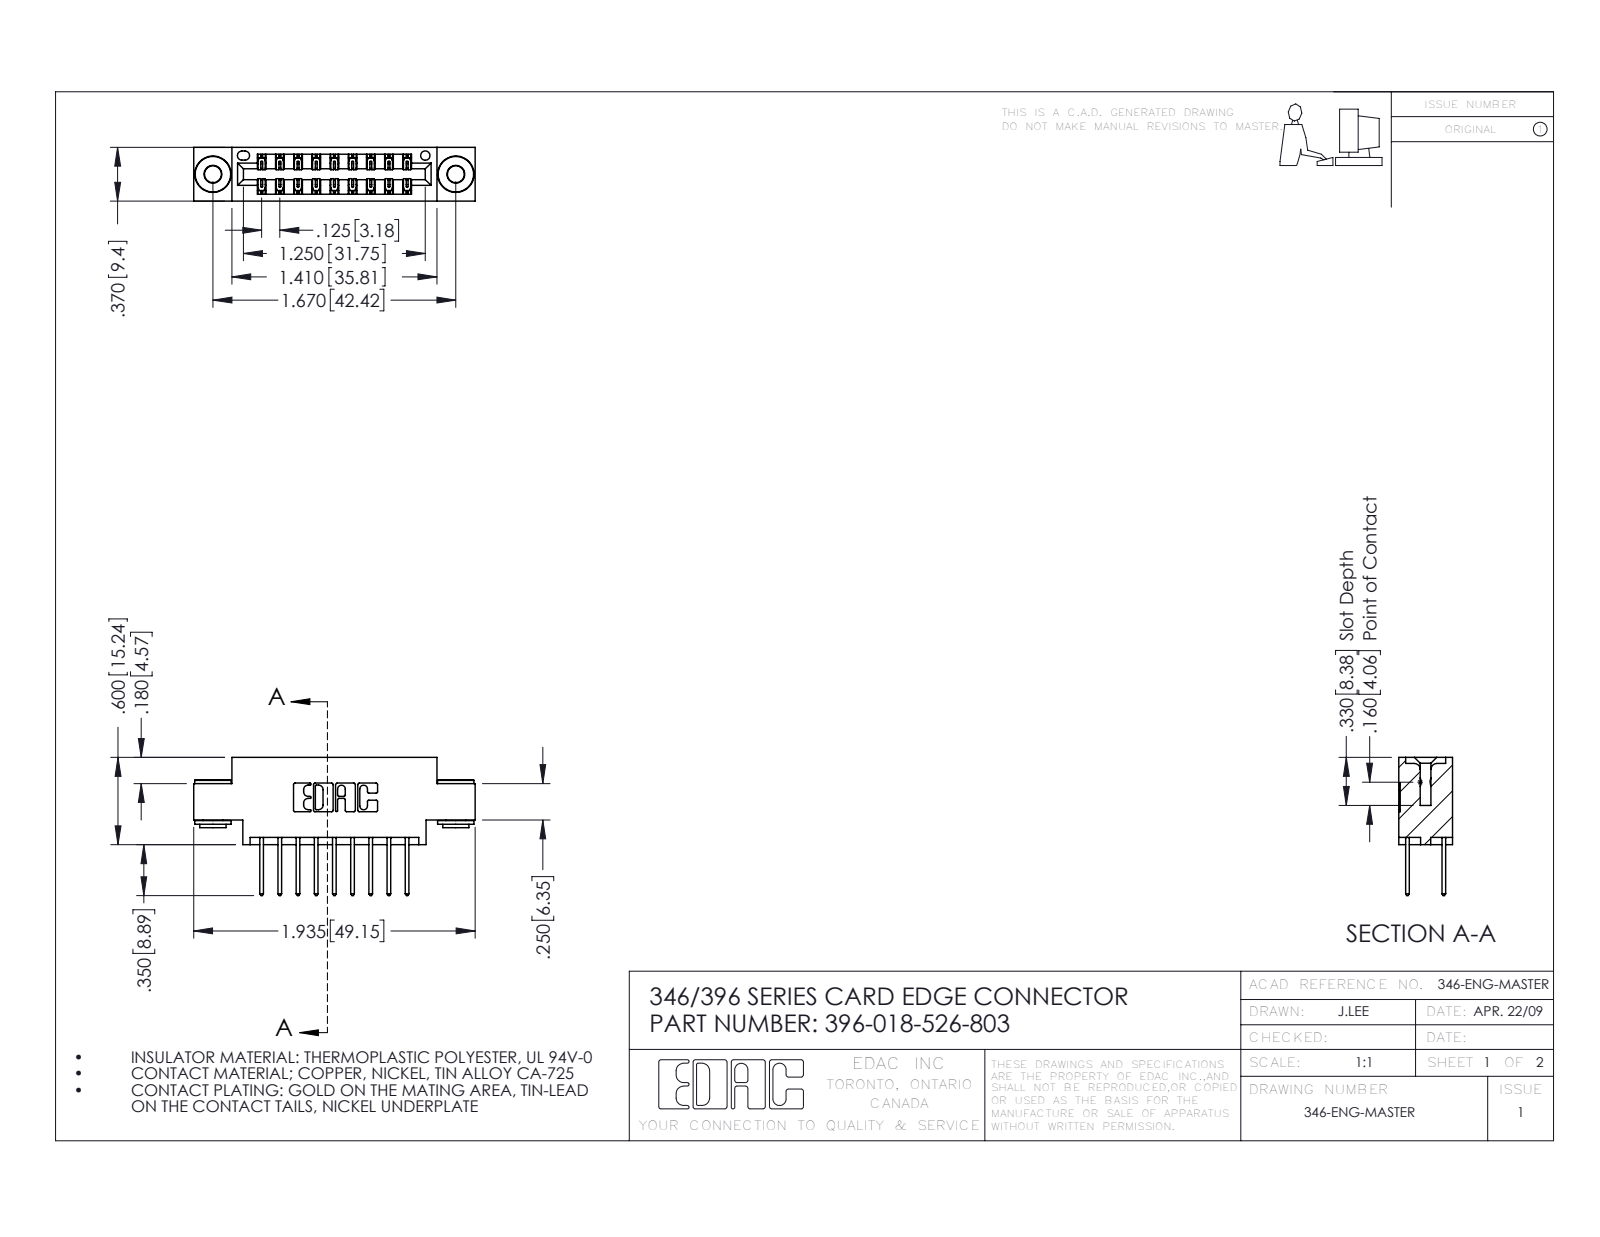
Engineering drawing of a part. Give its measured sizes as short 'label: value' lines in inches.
name: 346 Part_0.170 Offset - 0.156 Dia-TH; 345-292-001_345-293-126; 345-250-002_345-250-002-102; 396-018-526-803
written by: SolidWorks 2016 (CONFIG_CONTROL_DESIGN)
unit: in
bodies: 21 solids, 1100 faces (720 planar, 372 cylindrical, 8 other)
size: 1.935 × 0.95 × 0.37
volume: 0.27 in³; area: 9.451 in²
holes: 2× ⌀0.116, 2× ⌀0.156, 1× ⌀0.064
bosses: 2× ⌀0.25, 2× ⌀0.18, 2× ⌀0.136
rounds: 27× R0.006, 22× R0.01, 18× R0.01, 6× R0.007, 6× R0.031, 3× R0.026, 2× R0.014, 2× R0.022
face distances: 0.25, 0.048, 0.322, 0.37, 0.025, 0.072, 0.298, 0.275, 0.148, 0.222
hole spacings: 0.246, 1.465, 1.67
